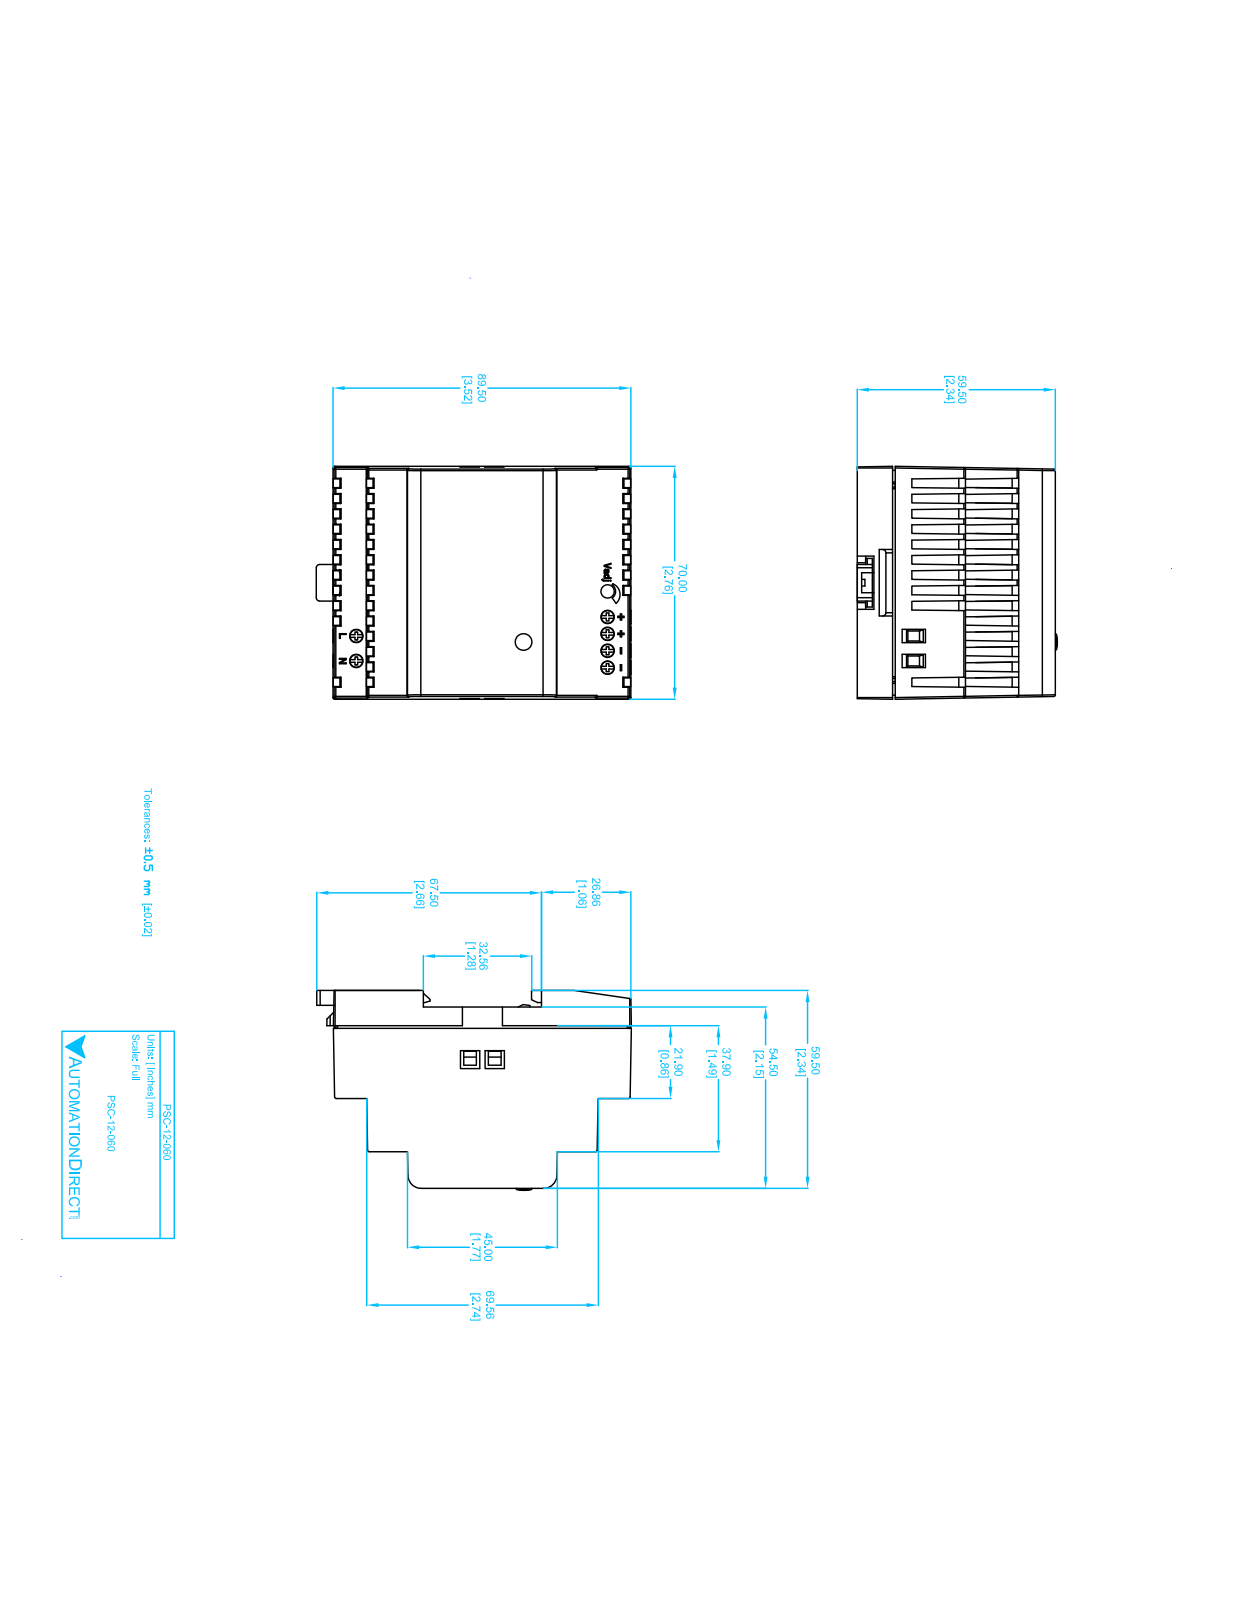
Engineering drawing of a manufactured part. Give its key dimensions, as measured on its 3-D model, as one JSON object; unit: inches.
{"part_name": "PSC-12-060", "step_written_by": "SolidWorks 2011 (CONFIG_CONTROL_DESIGN)", "units": "inches", "bodies": {"solids": 1, "faces": 709, "planar": 578, "cylindrical": 95, "other": 36}, "overall_size": [3.719, 2.759, 2.372], "volume_in3": 17.07, "surface_area_in2": 62.88, "round_holes": [[0.16, 7]], "round_bosses_or_shafts": [[0.2, 1]], "partial_cylinders_radius": [[0.02, 26], [0.04, 2], [0.16, 2]], "face_to_face_distances": [0.19, 0.595, 2.341, 2.151, 0.177, 0.419, 1.9, 1.71, 0.441, 2.759], "hole_center_spacings": [0.2, 0.4, 0.25, 0.3, 0.45, 0.6, 0.65, 0.85]}
